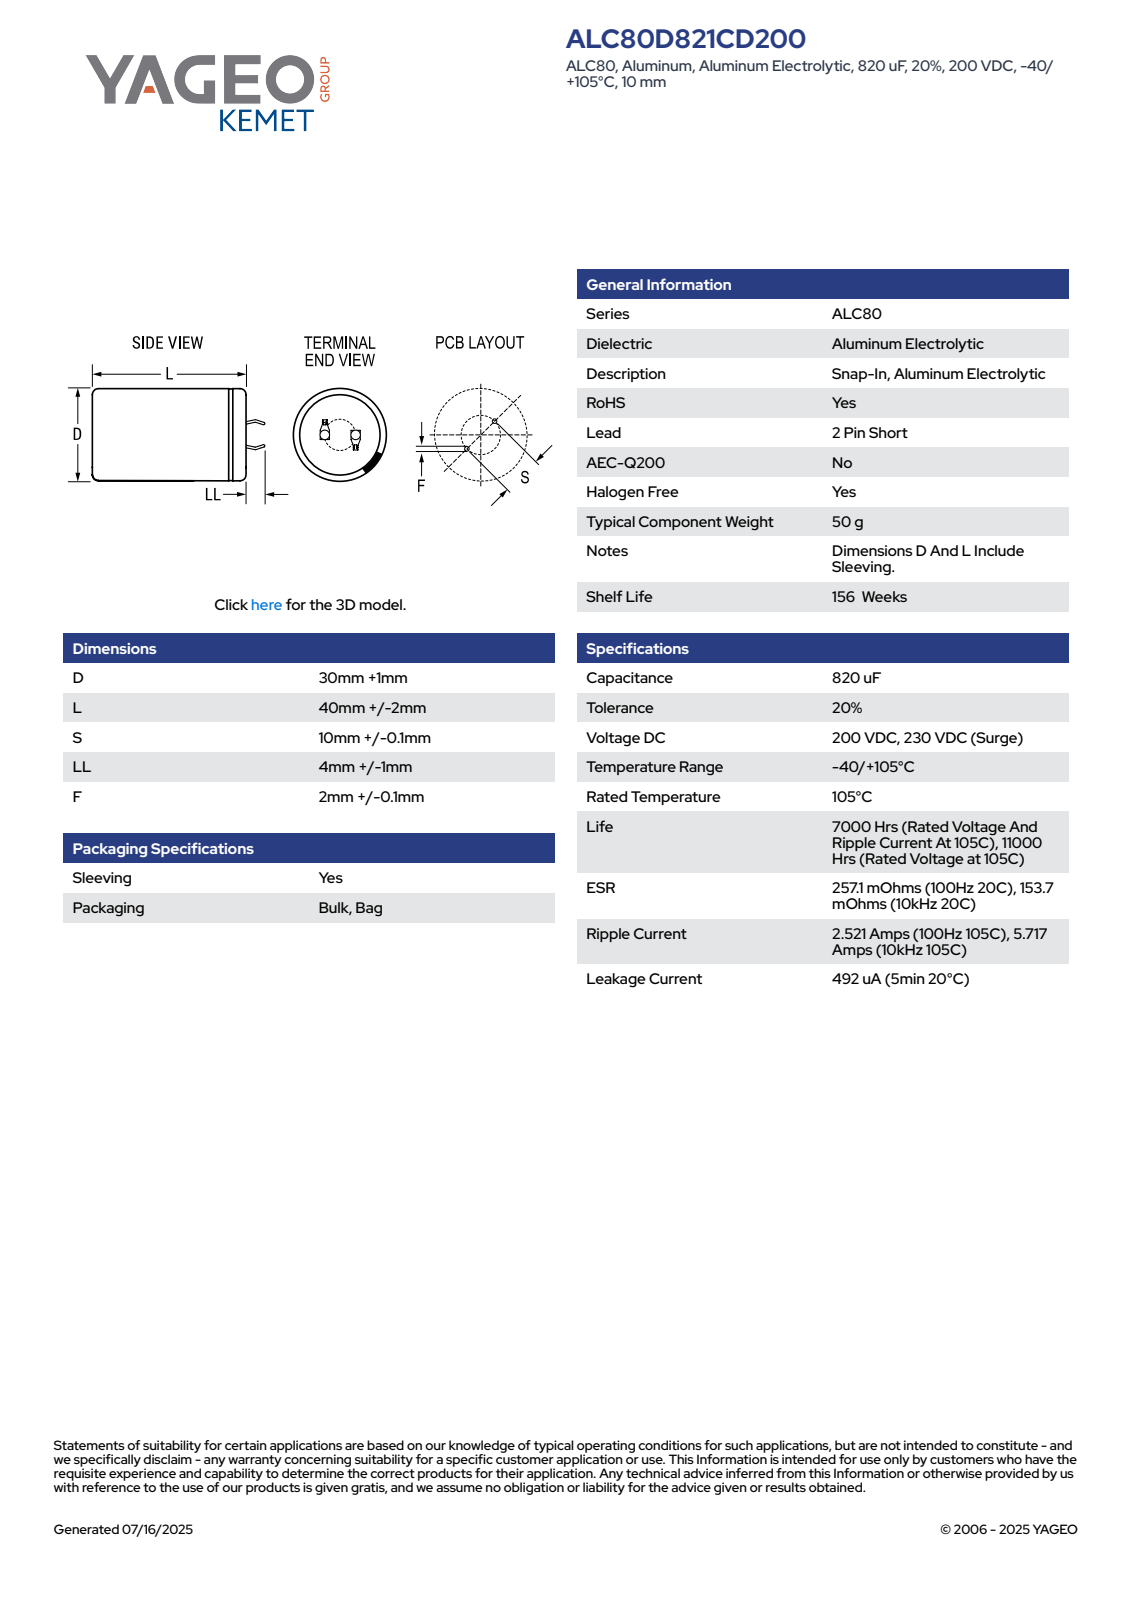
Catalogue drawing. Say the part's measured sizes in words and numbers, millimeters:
The part is named "CARS_K2P_30X40_D31L42S10LL5F2.1". Its 3-D file was written by "SolidWorks 2014 (AUTOMOTIVE_DESIGN)". It is 1 solid with 100 faces: 52 planar, 9 cylindrical and 39 other. Overall it measures 46.99 by 31 by 31 millimeters. Its volume is 31 365 cubic millimeters and its surface area 5 599 square millimeters. Round holes: 1 of diameter 27.43. Round bosses or shafts: 1 of diameter 31. Partial cylindrical surfaces (rounded edges, fillets, slot ends): 1 of radius 15.49. The main face-to-face distances are 41.99, 42.49, 0.5, 7.08, 0.6, 0.59, 7.6, 0.75, 1.35, 7.68.
